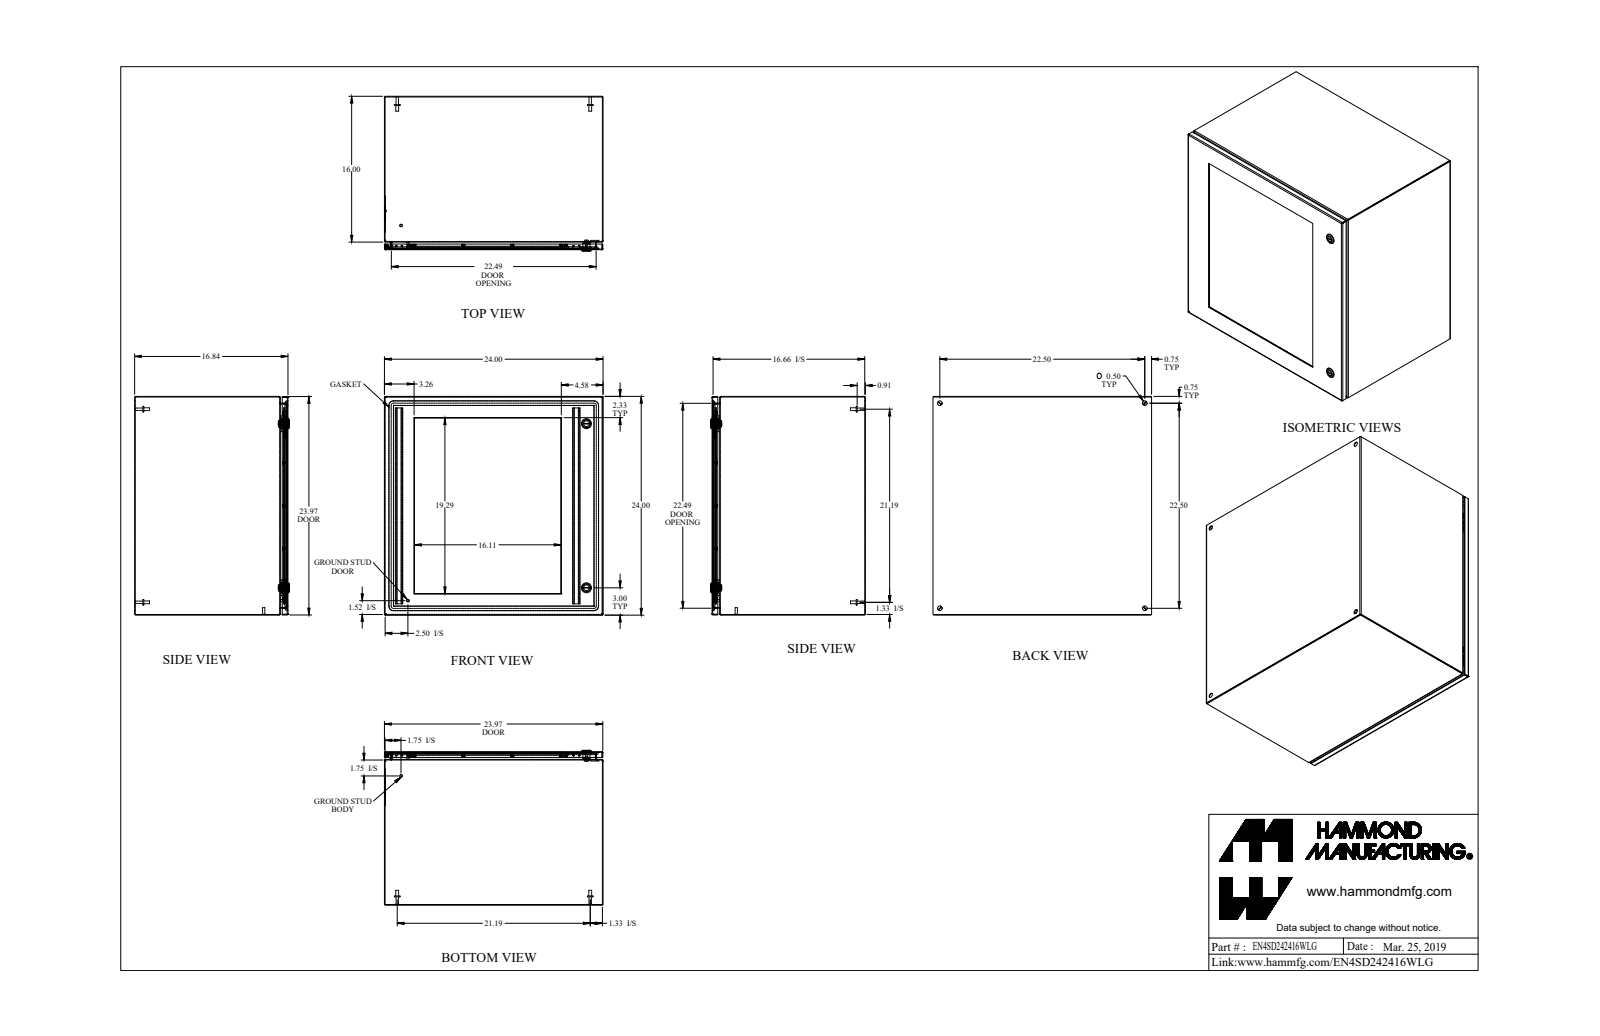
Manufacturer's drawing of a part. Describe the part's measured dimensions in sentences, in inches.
The part is named "EN4SD242416WLG". Its 3-D file was written by "SolidWorks 2019 (AUTOMOTIVE_DESIGN)". It is 74 solids with 1435 faces: 740 planar, 441 cylindrical and 254 other. Overall it measures 24 by 24 by 16.997 inches. Its volume is 285.6 cubic inches and its surface area 6 420 square inches. Round holes: 18 of diameter 0.13, 18 of diameter 0.25, 4 of diameter 0.5, 2 of diameter 0.232, 2 of diameter 0.625, 2 of diameter 0.785, 1 of diameter 0.172, 1 of diameter 0.24, 1 of diameter 0.242. Round bosses or shafts: 19 of diameter 0.226, 18 of diameter 0.368, 18 of diameter 0.164, 4 of diameter 0.625, 4 of diameter 0.313, 4 of diameter 0.27, 2 of diameter 1.1, 2 of diameter 0.525. Partial cylindrical surfaces (rounded edges, fillets, slot ends): 14 of radius 0.036, 14 of radius 0.108, 12 of radius 0.043, 12 of radius 0.081, 12 of radius 0.125, 12 of radius 0.312, 8 of radius 0.1, 4 of radius 0.006. The main face-to-face distances are 0.072, 23.928, 16.765, 23.856, 24, 16.693, 16.443, 0.25, 16.515, 0.322. The hole center spacings are 5.372, 17.781, 4.719, 19.57, 21.03, 5.372, 9.437, 10.743.
